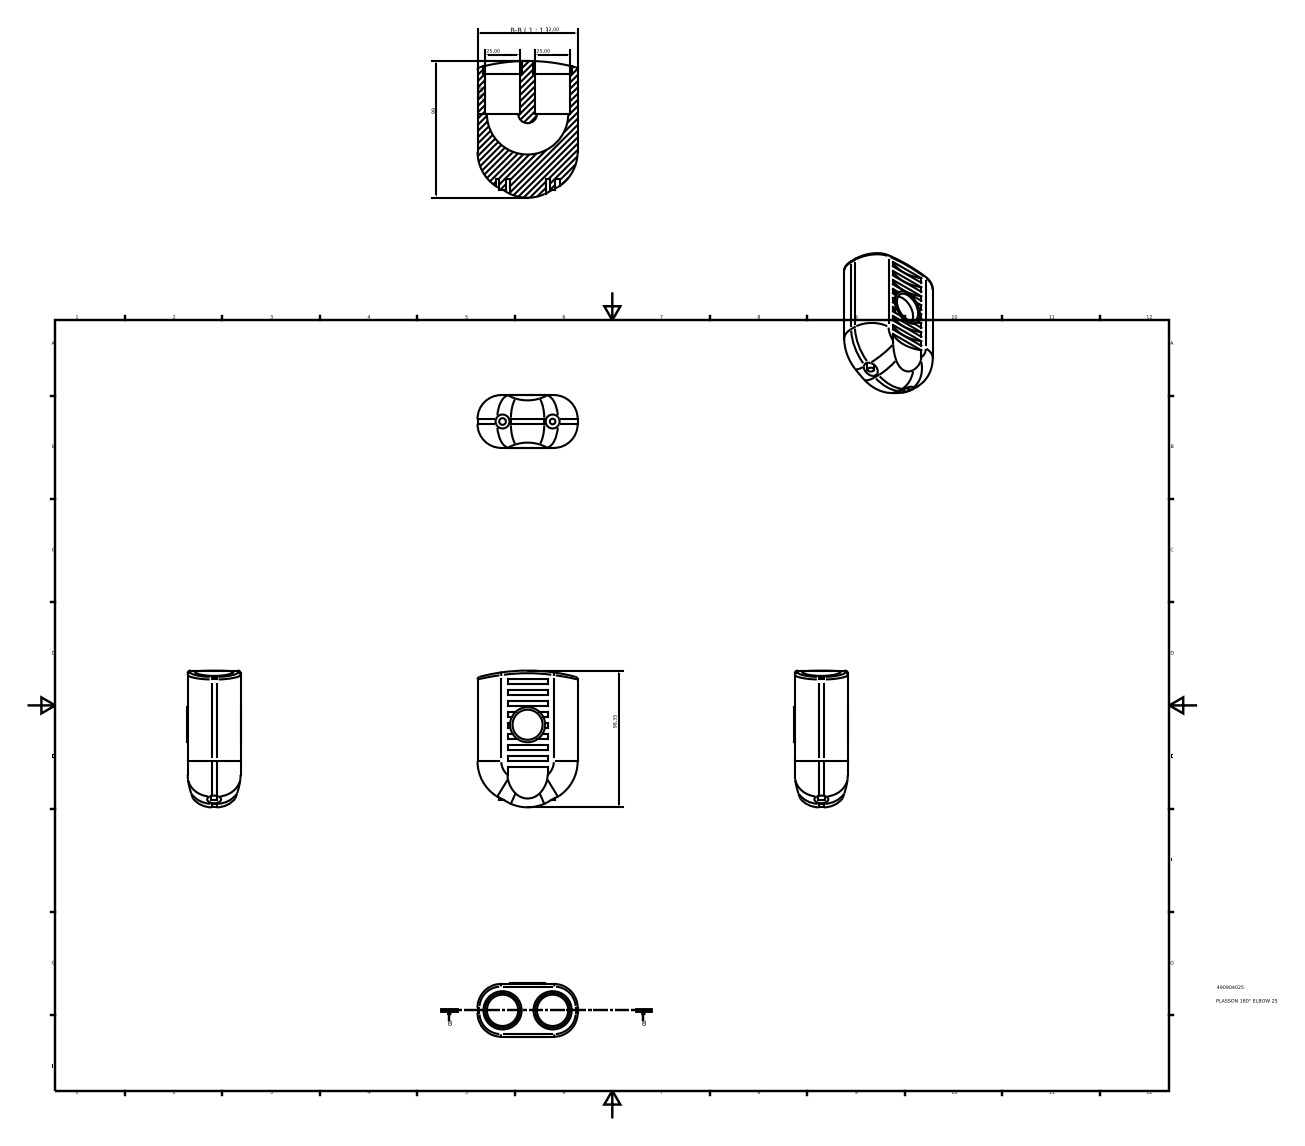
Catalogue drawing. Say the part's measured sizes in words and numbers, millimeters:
The part is named "490904025". Its 3-D file was written by "Autodesk Inventor 2015 (AUTOMOTIVE_DESIGN)". It is 1 solid with 127 faces: 62 planar, 48 cylindrical and 17 other. Overall it measures 98.35 by 72 by 38.76 millimeters. Its volume is 146 219 cubic millimeters and its surface area 32 830 square millimeters. Round holes: 2 of diameter 10, 2 of diameter 25, 2 of diameter 27.5, 1 of diameter 21.6. Round bosses or shafts: 1 of diameter 25.2, 1 of diameter 4.8, 1 of diameter 4. Partial cylindrical surfaces (rounded edges, fillets, slot ends): 4 of radius 17.1, 3 of radius 29.7, 2 of radius 1.9, 2 of radius 29.18, 2 of radius 83.11, 1 of radius 133.38. The main face-to-face distances are 3.96, 38, 7.92, 11.88, 43.56, 47.52, 4.75, 33.25, 39.6, 51.48. The hole center spacings are 36.
